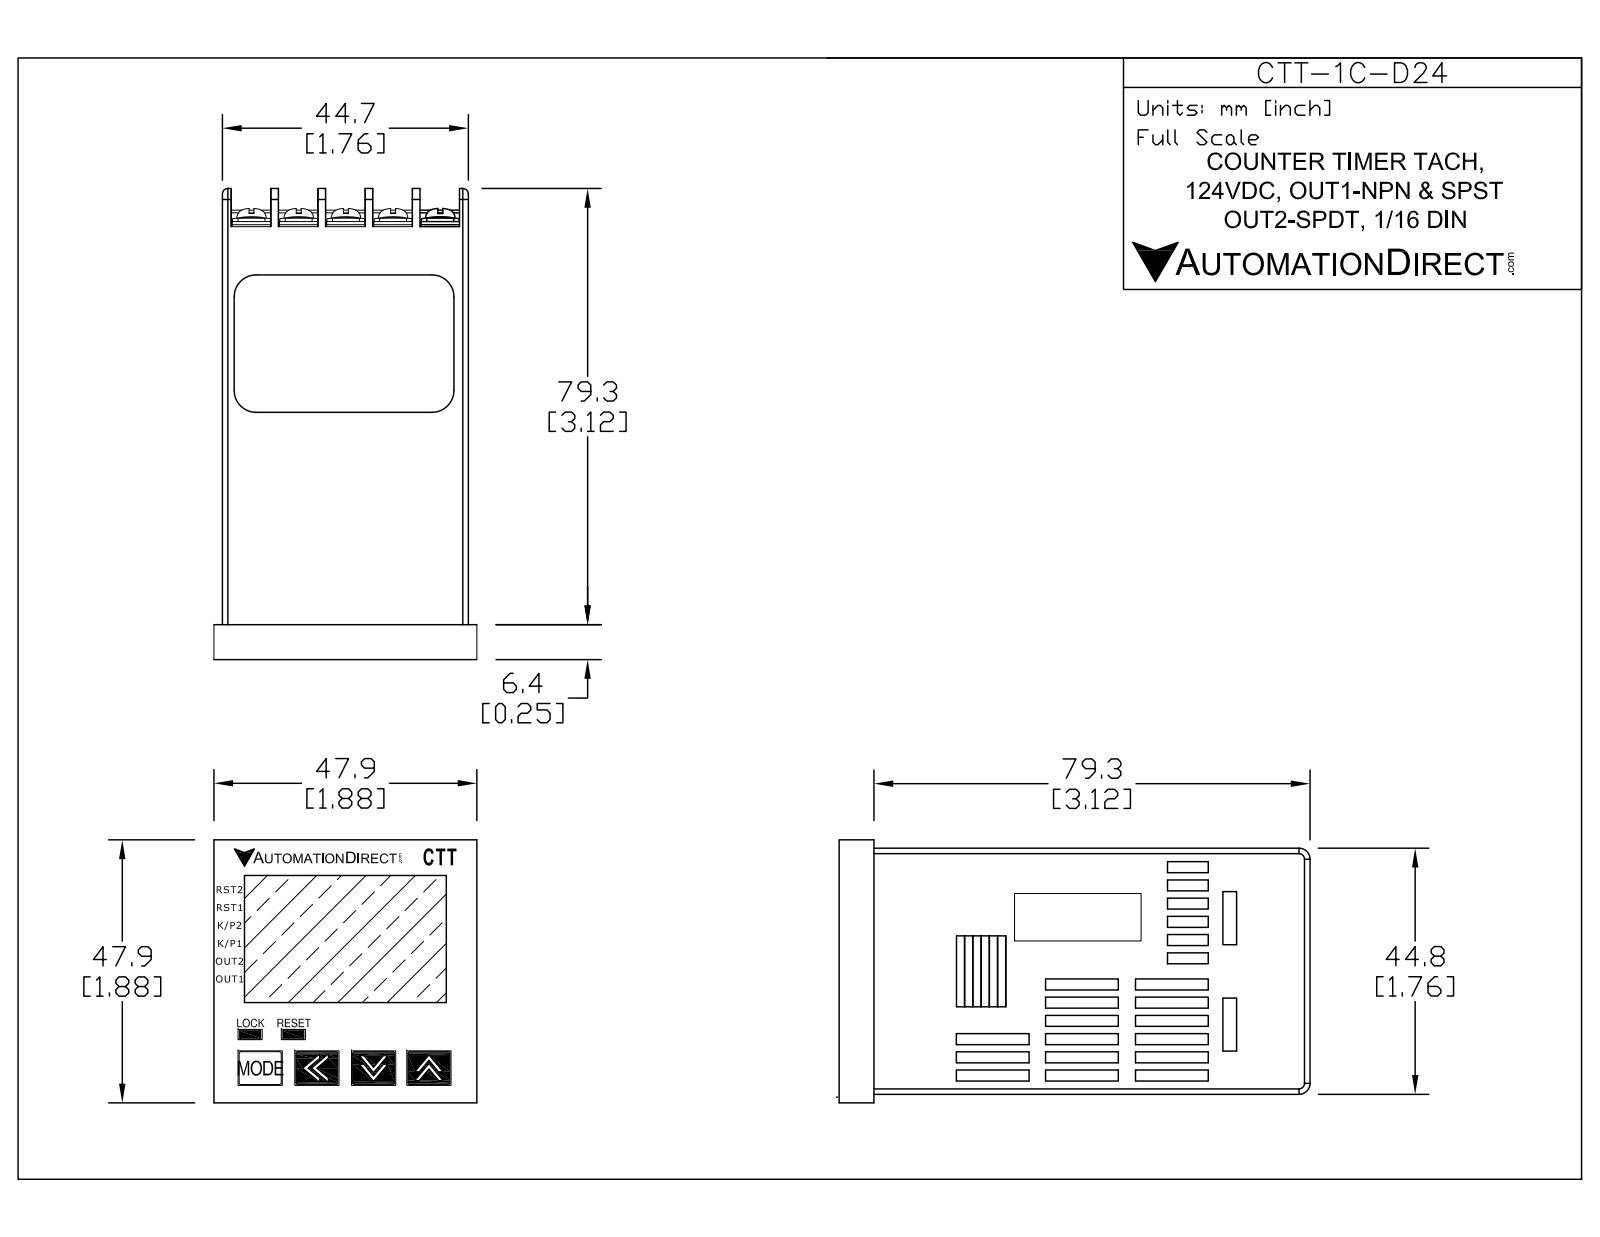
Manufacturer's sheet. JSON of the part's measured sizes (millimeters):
{"part_name": "CTT-1C-D24", "step_written_by": "SolidWorks 2017 (AUTOMOTIVE_DESIGN)", "units": "millimeters", "bodies": {"solids": 4, "faces": 1082, "planar": 701, "cylindrical": 240, "other": 141}, "overall_size": [86.7, 56.4, 48], "volume_mm3": 169900, "surface_area_mm2": 33810, "round_holes": [[3, 2]], "round_bosses_or_shafts": [[5.3, 15], [5.3, 2], [2.9, 2]], "partial_cylinders_radius": [[0.3, 92], [0.3, 16], [0.2, 8], [1, 6], [1.1, 4], [0.8, 2], [3, 2], [4, 2]], "face_to_face_distances": [44.8, 8.6, 1.2, 46.1, 17.2, 7.2, 15.8, 1.4, 47.3, 1.5], "hole_center_spacings": [63.7]}
